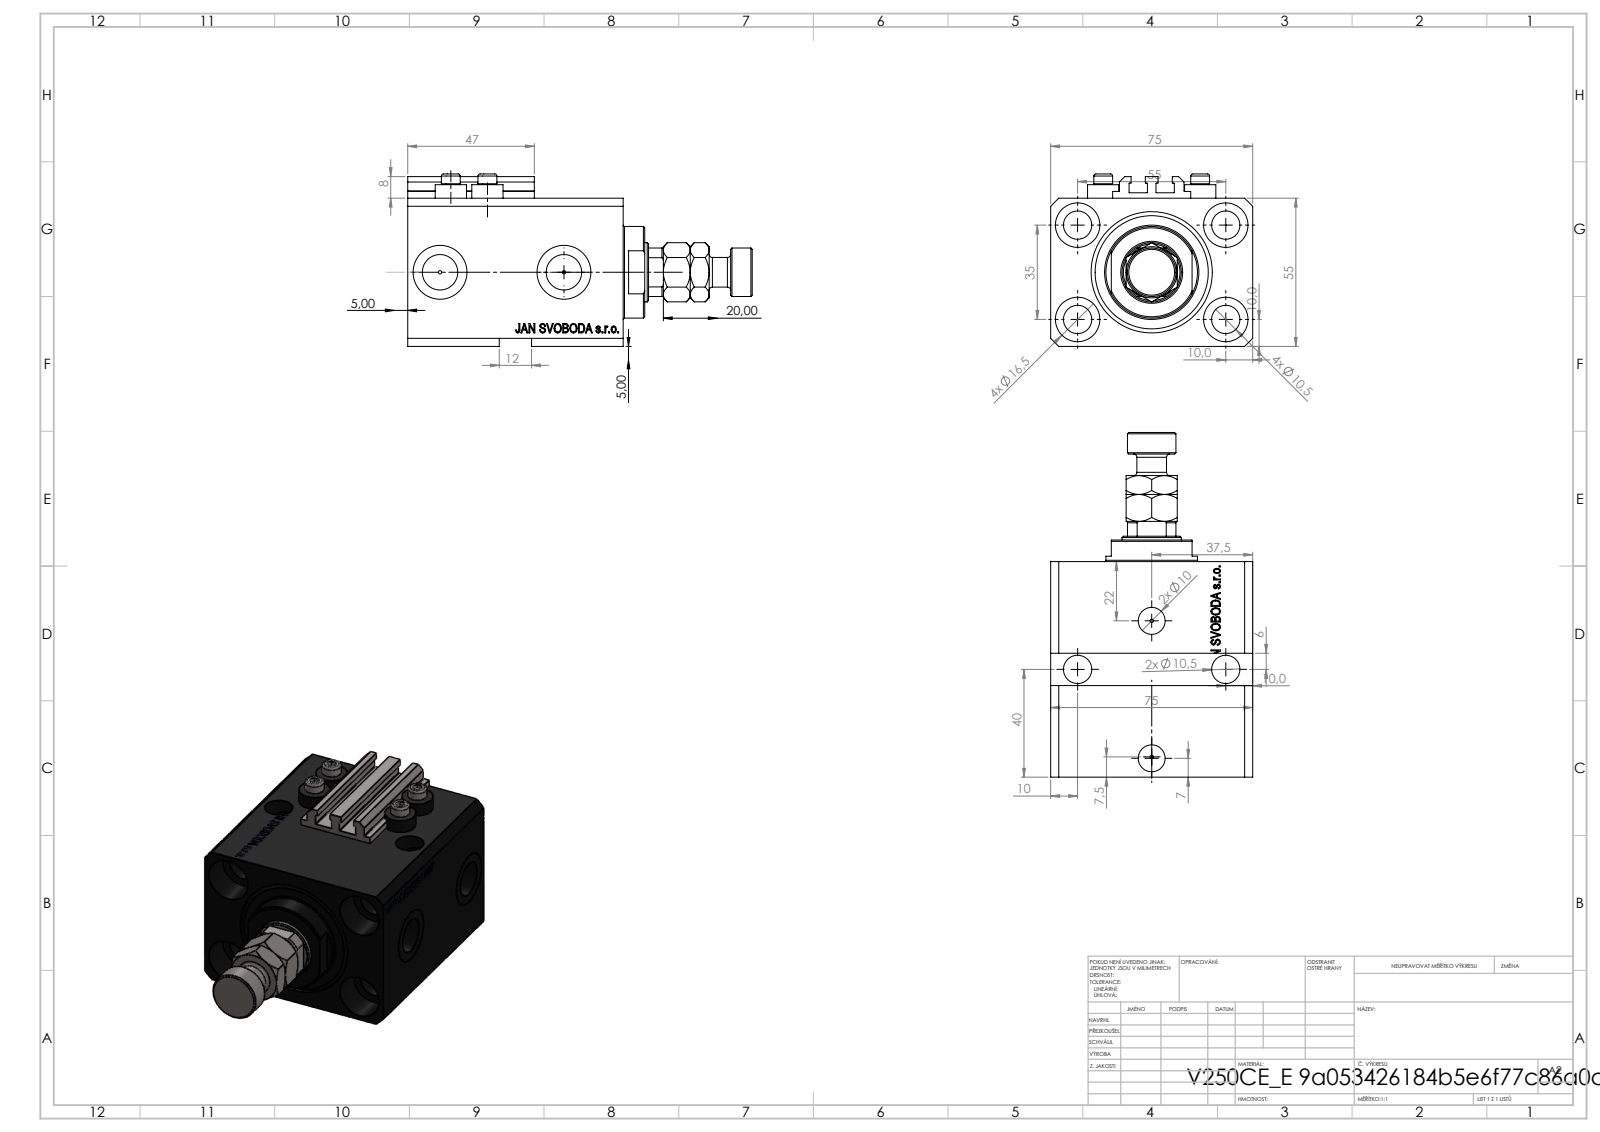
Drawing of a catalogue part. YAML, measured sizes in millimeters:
part_name: "MFA; V250CE_C_VCP; V250CE_VC_E; ALLEN BOLT V250CE (+1 more)"
step_written_by: "SolidWorks 2019 (CONFIG_CONTROL_DESIGN)"
units: millimeters
bodies: {solids: 9, faces: 1132, planar: 534, cylindrical: 142, other: 456}
overall_size: [128, 75, 64]
volume: 288342
surface_area: 78309
round_holes:
  - {diameter: 10.5, count: 7}
  - {diameter: 1.25, count: 4}
  - {diameter: 4, count: 4}
  - {diameter: 16.5, count: 4}
  - {diameter: 10, count: 2}
  - {diameter: 13.16, count: 2}
  - {diameter: 20, count: 2}
  - {diameter: 22, count: 1}
  - {diameter: 32, count: 1}
  - {diameter: 45, count: 1}
round_bosses_or_shafts:
  - {diameter: 11.6, count: 4}
  - {diameter: 7, count: 4}
  - {diameter: 34, count: 1}
  - {diameter: 18, count: 1}
  - {diameter: 11, count: 1}
partial_cylinders:
  - {radius: 0.2, count: 10}
  - {radius: 10.5, count: 1}
face_to_face_distances: [55, 75, 15, 65, 80, 9.9, 55.1, 3, 70.1, 54]
hole_center_spacings: [32.6, 55, 13.6, 14.09, 19.89, 20.12, 25.81, 28.48]
